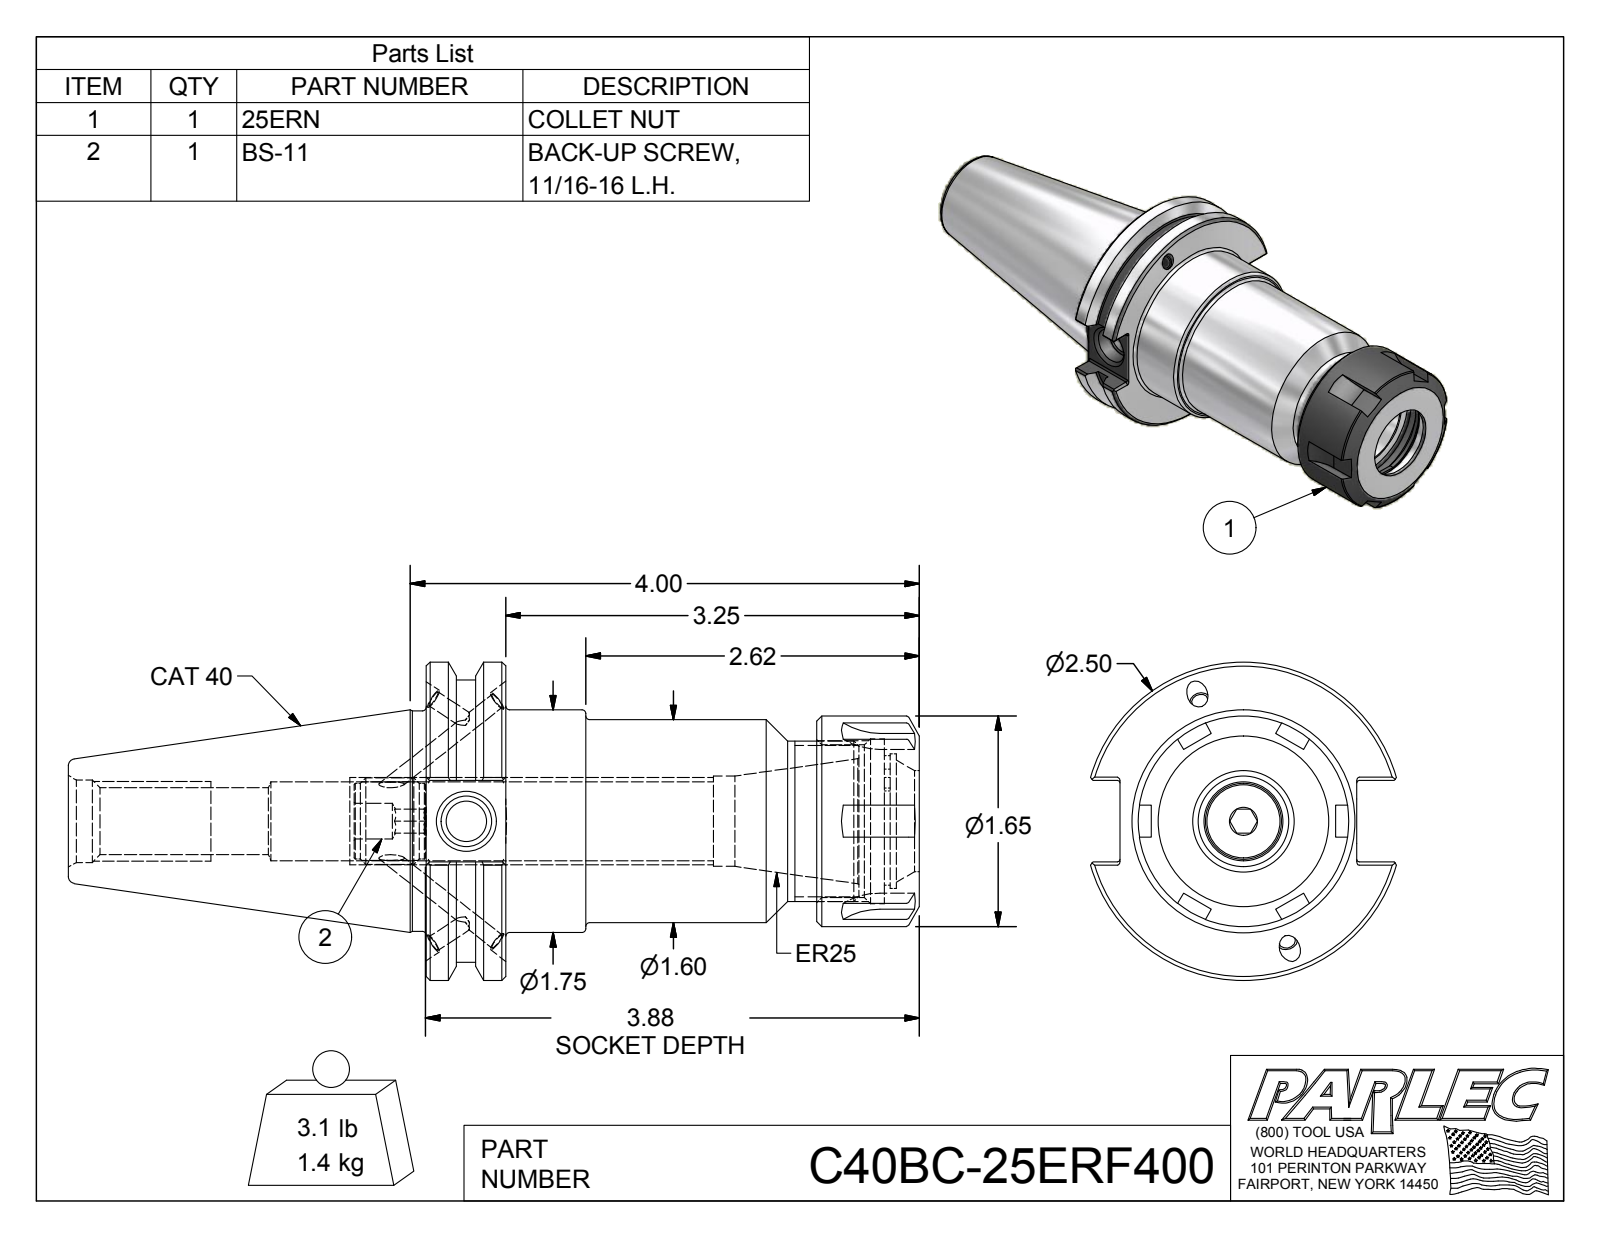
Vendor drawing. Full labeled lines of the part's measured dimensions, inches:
Part name (STEP PRODUCT): C40BCB-25ER4-1; 029-965; 25ERN; BS-11 (+1 more)
STEP written by: Autodesk Inventor 2016 (AUTOMOTIVE_DESIGN)
Units: inches
Bodies: 7 solids, 267 faces (120 planar, 71 cylindrical, 76 other)
Overall size (bounding box): 6.687 × 2.5 × 2.404
Volume: 11.12 in³ · Surface area: 64.71 in²
Round holes (diameter × count): ⌀0.13 ×4, ⌀0.161 ×4, ⌀0.28 ×1, ⌀0.315 ×1, ⌀0.399 ×1, ⌀0.527 ×1, ⌀0.62 ×1, ⌀0.648 ×1, ⌀0.71 ×1, ⌀0.8 ×1, ⌀1.201 ×1, ⌀1.294 ×1
Round bosses / shafts (diameter × count): ⌀0.165 ×4, ⌀0.157 ×4, ⌀2.5 ×1, ⌀2.219 ×1, ⌀1.75 ×1, ⌀1.73 ×1, ⌀1.654 ×1, ⌀1.595 ×1
Partial cylindrical surfaces — rounded edges, fillets, slot ends (radius × count): R0.02 ×24, R0.472 ×1, R0.514 ×1, R0.529 ×1
Main face-to-face distances: 0.625, 3.875, 3.25, 3.065, 2.44, 0.81, 3.596, 2.97, 0.531, 0.28
